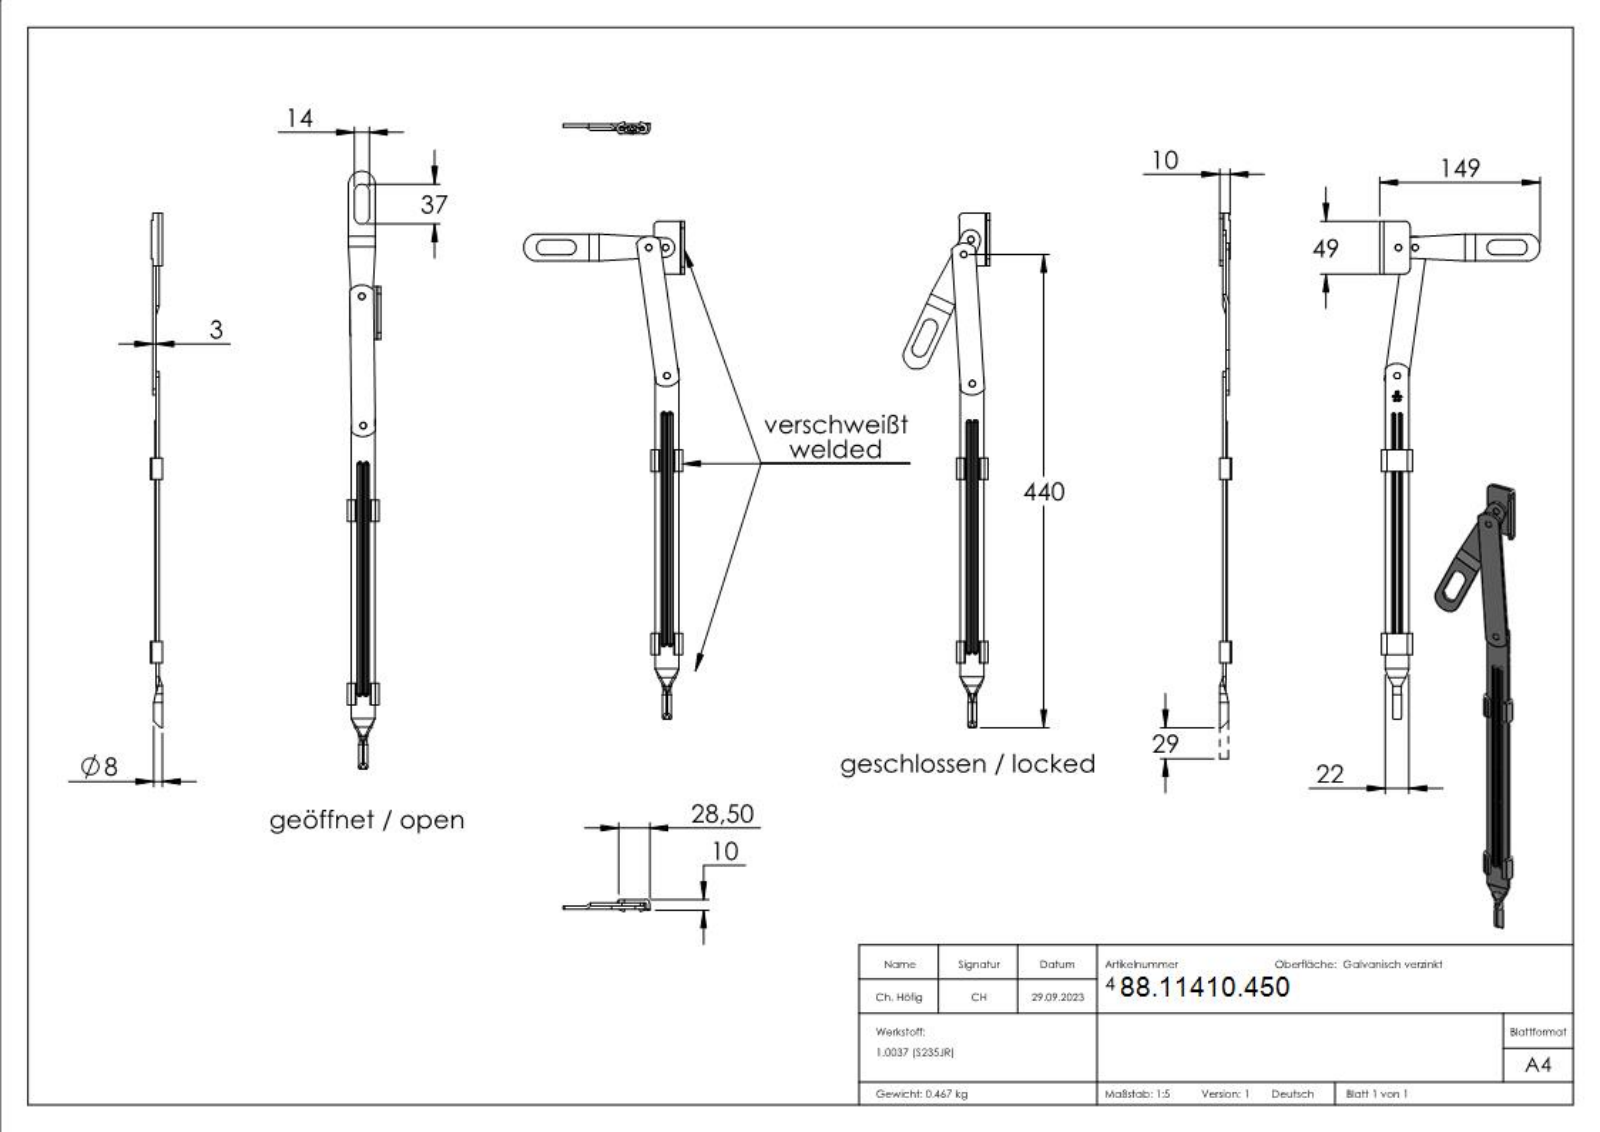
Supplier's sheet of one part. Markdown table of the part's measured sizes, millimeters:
| quantity | value |
| --- | --- |
| part name | 410-x00 Teil1_410-450 Teil1; 410-450; 410-x00 Teil3_410-x00 Teil3; 410-x00 Teil5_410-x00 Teil5 (+3 more) |
| STEP written by | SolidWorks 2018 (CONFIG_CONTROL_DESIGN) |
| units | millimeters |
| bodies | 9 solids, 393 faces (208 planar, 47 cylindrical, 138 other) |
| overall size | 462.32 × 149 × 11 |
| volume | 48 538 mm³ |
| surface area | 39 025 mm² |
| round holes (diameter × count) | 6 × 3, 4 × 1 |
| round bosses / shafts (diameter × count) | 5.9 × 3, 8 × 1 |
| partial cylindrical surfaces (radius × count) | 0.5 × 12, 2 × 6, 5 × 4, 7 × 2, 15 × 2, 1 × 1, 3 × 1, 4 × 1 |
| main face-to-face distances | 3, 6, 9, 22, 4, 1, 2, 7, 5, 24.25 |
| hole center spacings | 15.5, 118.84, 120 |
